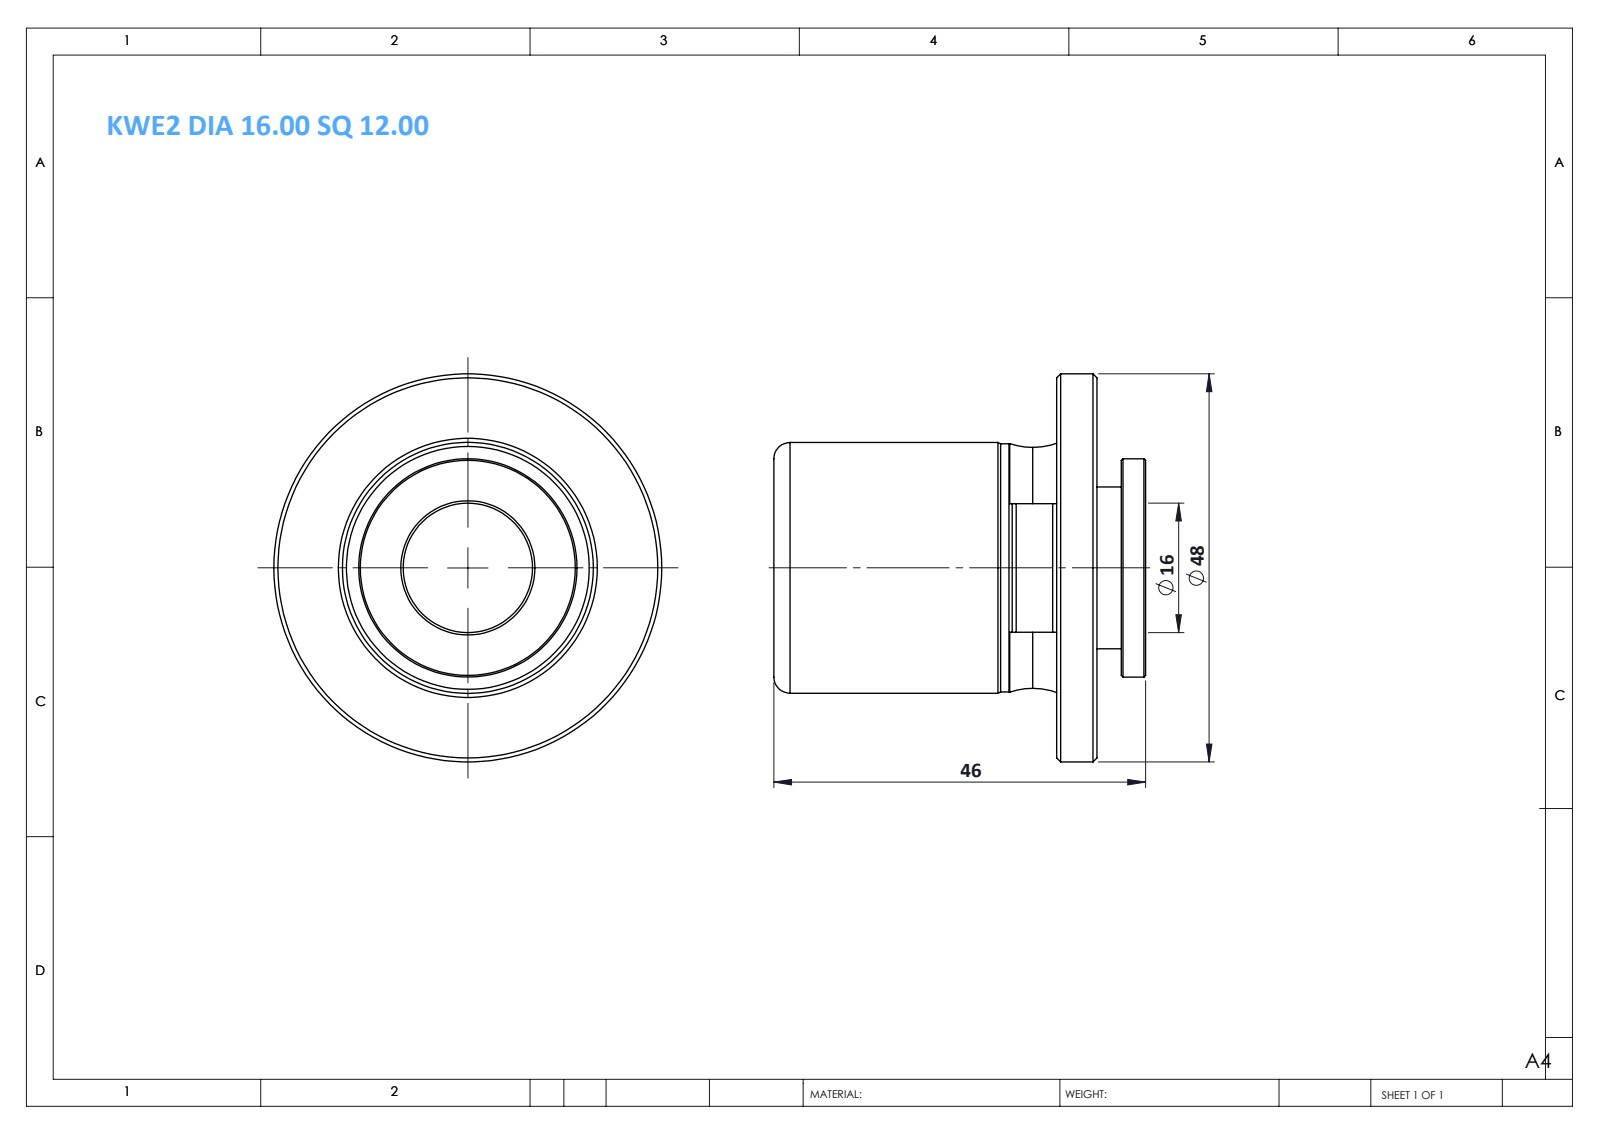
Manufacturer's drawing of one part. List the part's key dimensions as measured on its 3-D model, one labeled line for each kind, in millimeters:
Part name (STEP PRODUCT): KWE2 DIA 16.00 SQ 12.50
STEP written by: SolidWorks 2014 (CONFIG_CONTROL_DESIGN)
Units: millimetres
Bodies: 1 solid, 61 faces (13 planar, 18 cylindrical, 30 other)
Overall size (bounding box): 48 × 48 × 46
Volume: 32 956 mm³ · Surface area: 10 150 mm²
Round holes (diameter × count): ⌀16 ×1
Round bosses / shafts (diameter × count): ⌀48 ×1, ⌀31 ×1, ⌀30.7 ×1, ⌀27 ×1, ⌀20 ×1
Partial cylindrical surfaces — rounded edges, fillets, slot ends (radius × count): R15.53 ×1, R19.9 ×1
Main face-to-face distances: 5, 35, 40, 3, 46, 11, 6, 43, 8, 18
